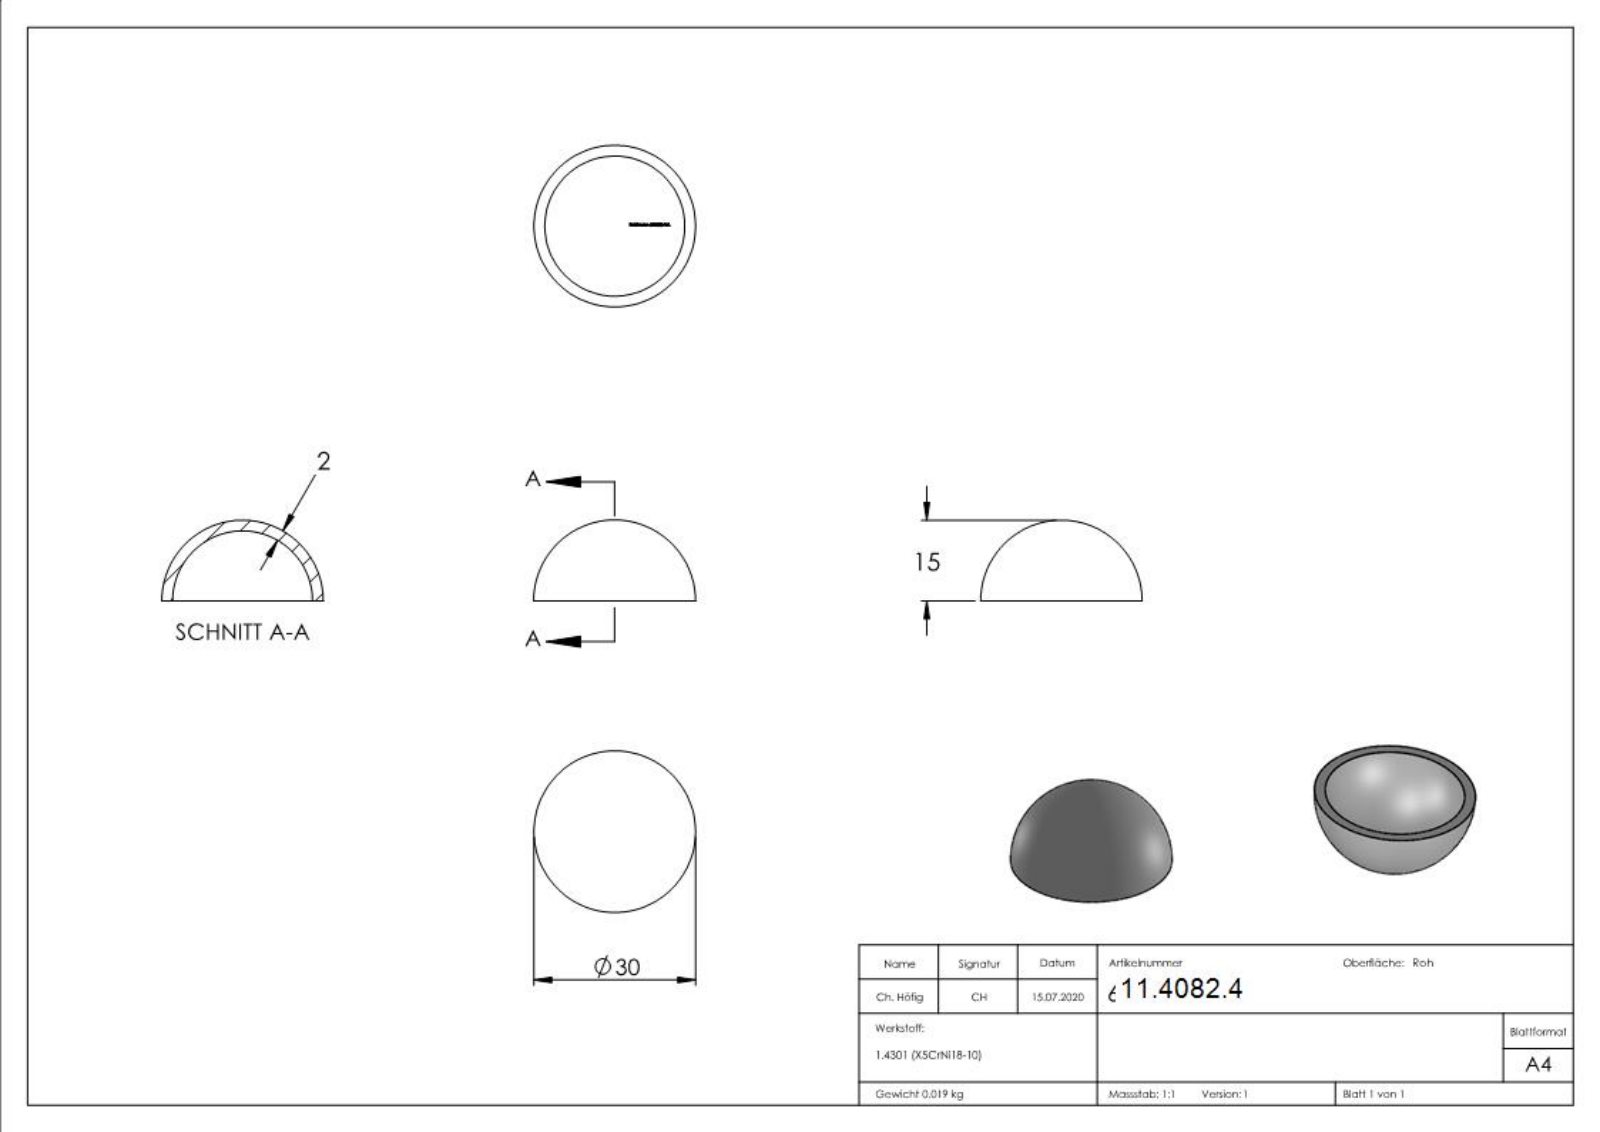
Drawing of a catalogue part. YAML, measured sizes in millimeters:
part_name: "620030-VA"
step_written_by: "SolidWorks 2018 (CONFIG_CONTROL_DESIGN)"
units: millimeters
bodies: {solids: 1, faces: 220, planar: 89, cylindrical: 0, other: 131}
overall_size: [30, 30, 15]
volume: 2467
surface_area: 2656
face_to_face_distances: [0.45, 0.5, 0.53, 0.61, 1.19, 0.31, 0.55, 0.81, 0.85, 1.31]
